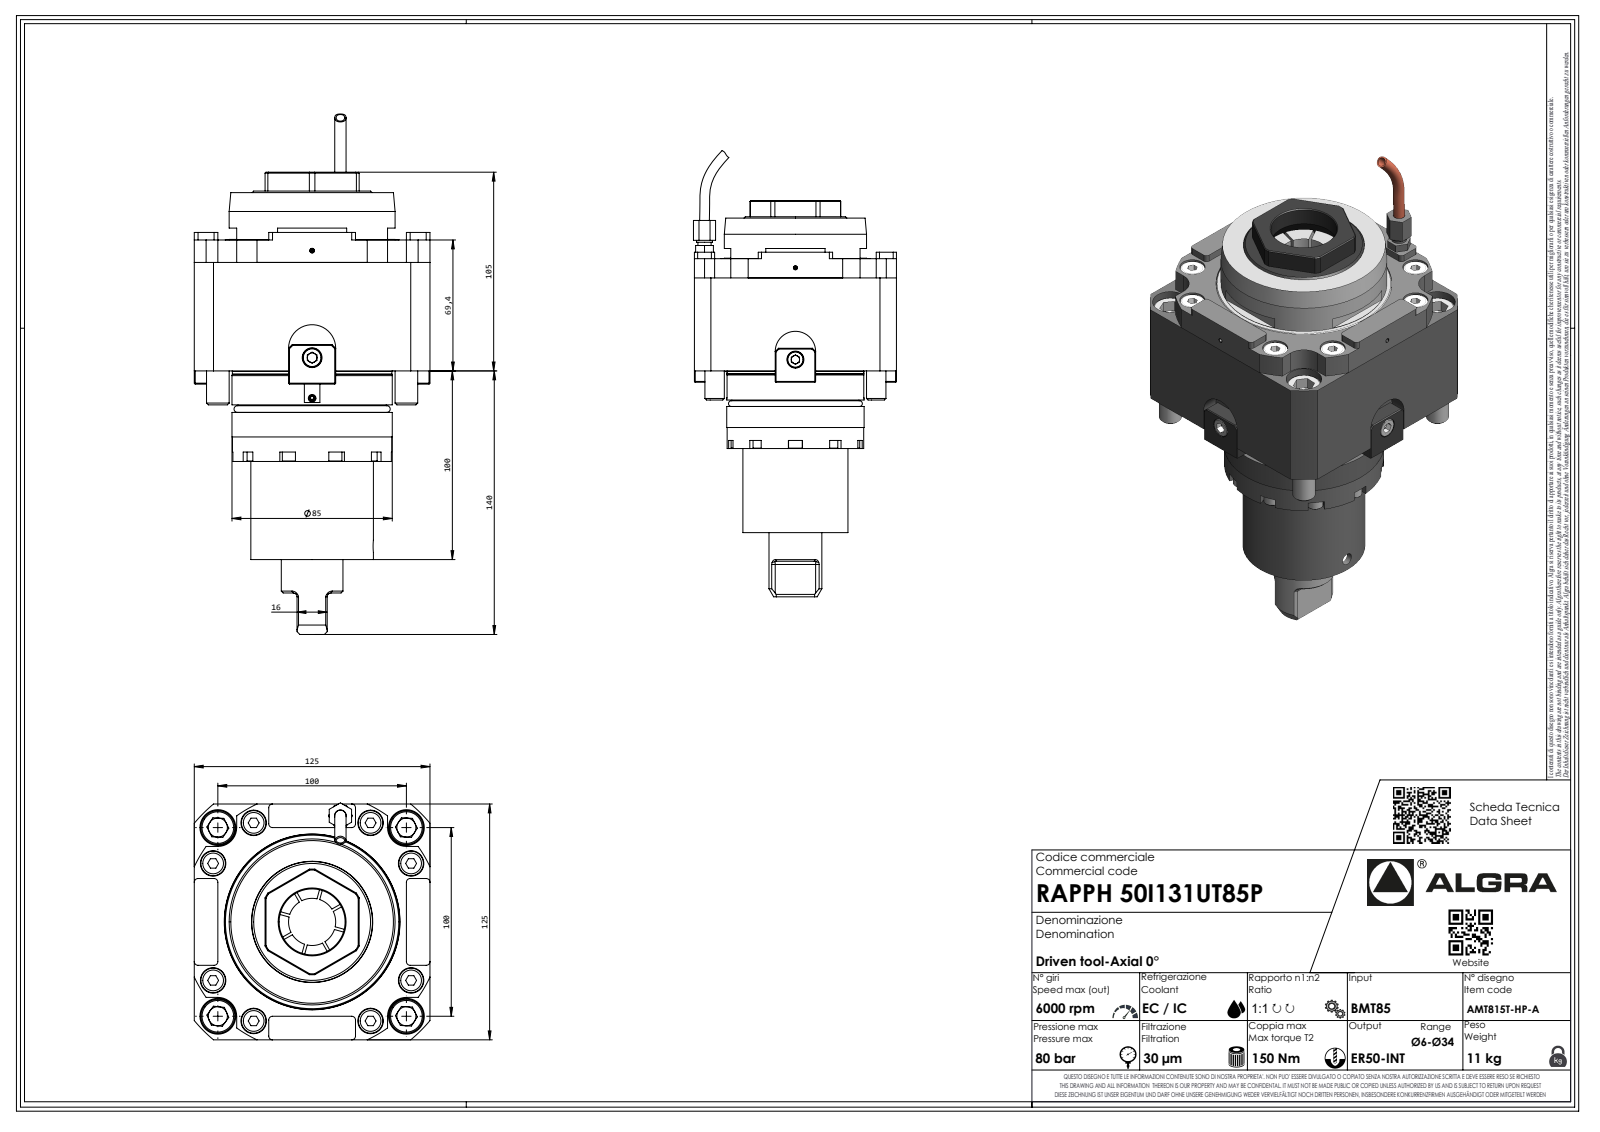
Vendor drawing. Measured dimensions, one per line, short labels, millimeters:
name: RAPPH50I131UT85P
written by: SolidWorks 2023 (AUTOMOTIVE_DESIGN)
unit: mm
bodies: 1 solid, 596 faces (401 planar, 80 cylindrical, 115 other)
size: 275.99 × 125.59 × 125
volume: 1 719 000 mm³; area: 107 858 mm²
holes: 1× ⌀2.1
bosses: 4× ⌀12, 1× ⌀88, 1× ⌀85, 1× ⌀65, 1× ⌀32.7, 1× ⌀9.8, 1× ⌀8.15, 1× ⌀6.37
rounds: 22× R2, 7× R0.33, 7× R0.52, 7× R3.7, 4× R10, 1× R0.21, 1× R28, 1× R69
face distances: 125, 69.5, 48, 25, 100, 94.5, 169.5, 194.5, 52, 117.5
